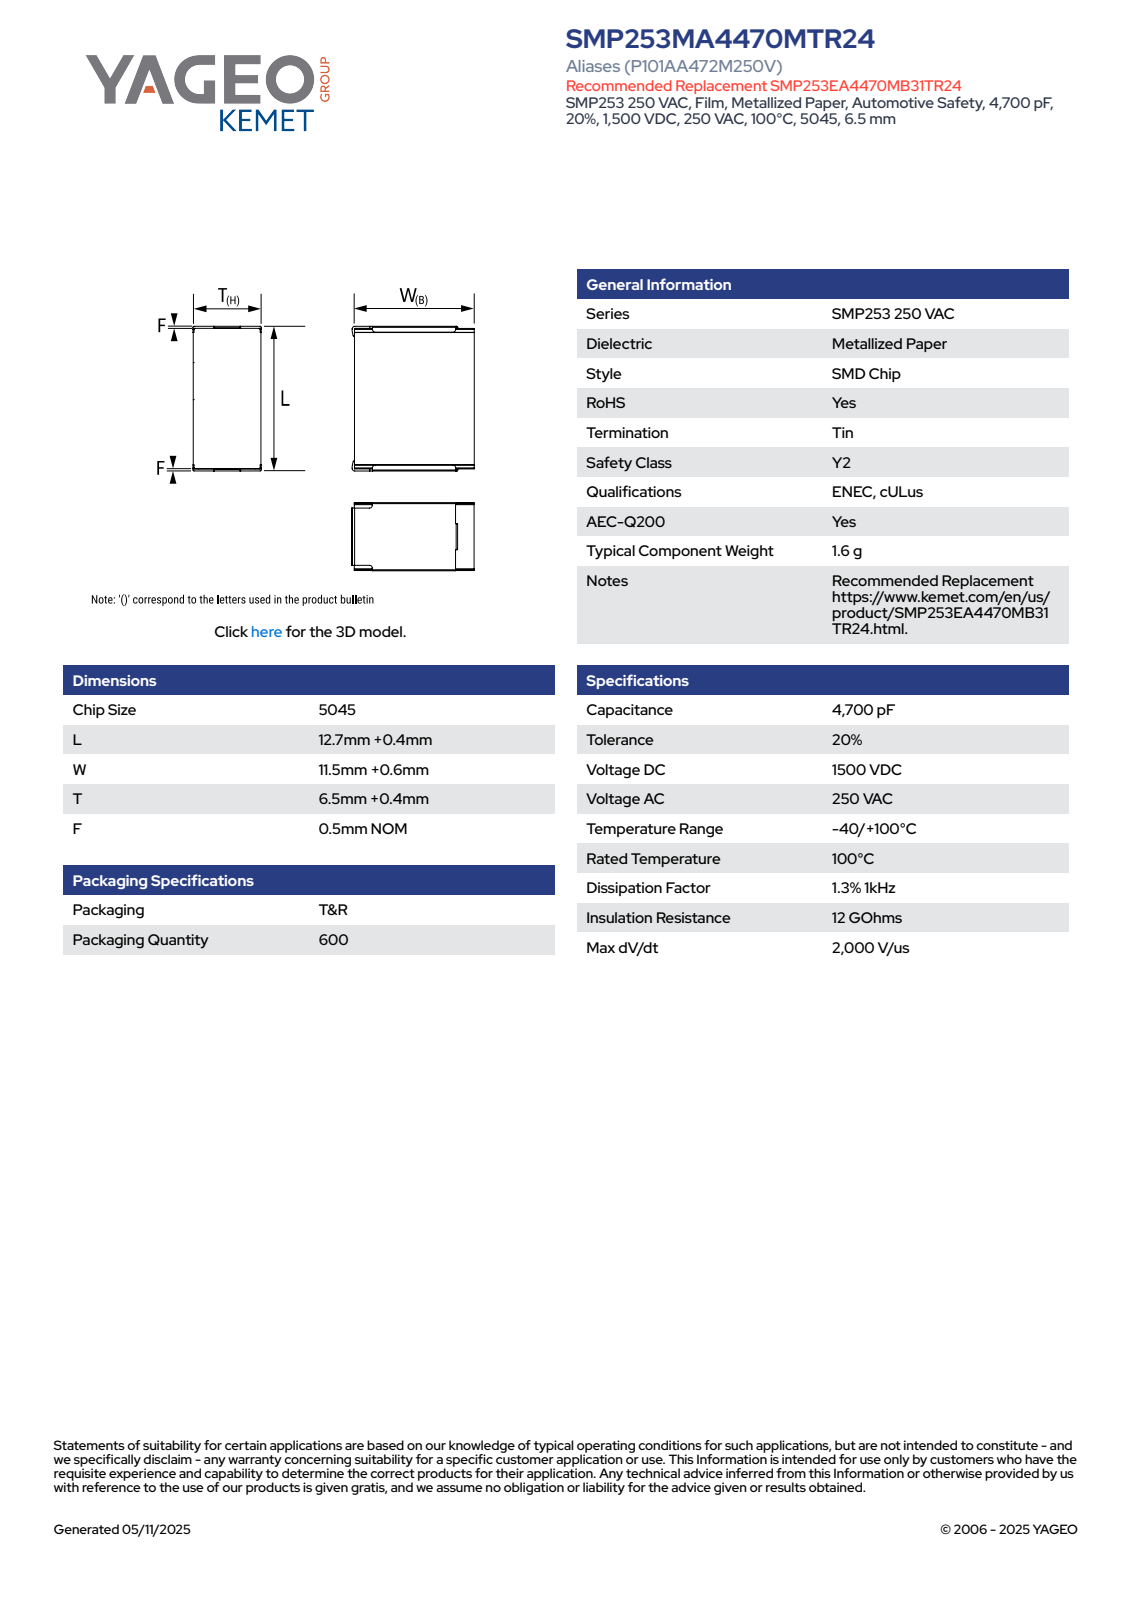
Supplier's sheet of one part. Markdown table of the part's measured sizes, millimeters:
| quantity | value |
| --- | --- |
| part name | CFS_KSTD_5045_L12.9W11.7T6.7F0.5 |
| STEP written by | SolidWorks 2021 (AUTOMOTIVE_DESIGN) |
| units | millimeters |
| bodies | 4 solids, 117 faces (103 planar, 14 cylindrical, 0 other) |
| overall size | 12.9 × 12.09 × 7.04 |
| volume | 978 mm³ |
| surface area | 667 mm² |
| partial cylindrical surfaces (radius × count) | 0.4 × 10, 0.45 × 4 |
| main face-to-face distances | 6.7, 11.23, 12.9, 0.5, 12.4, 6.87, 11.9, 0.47, 7.04, 12.09 |
